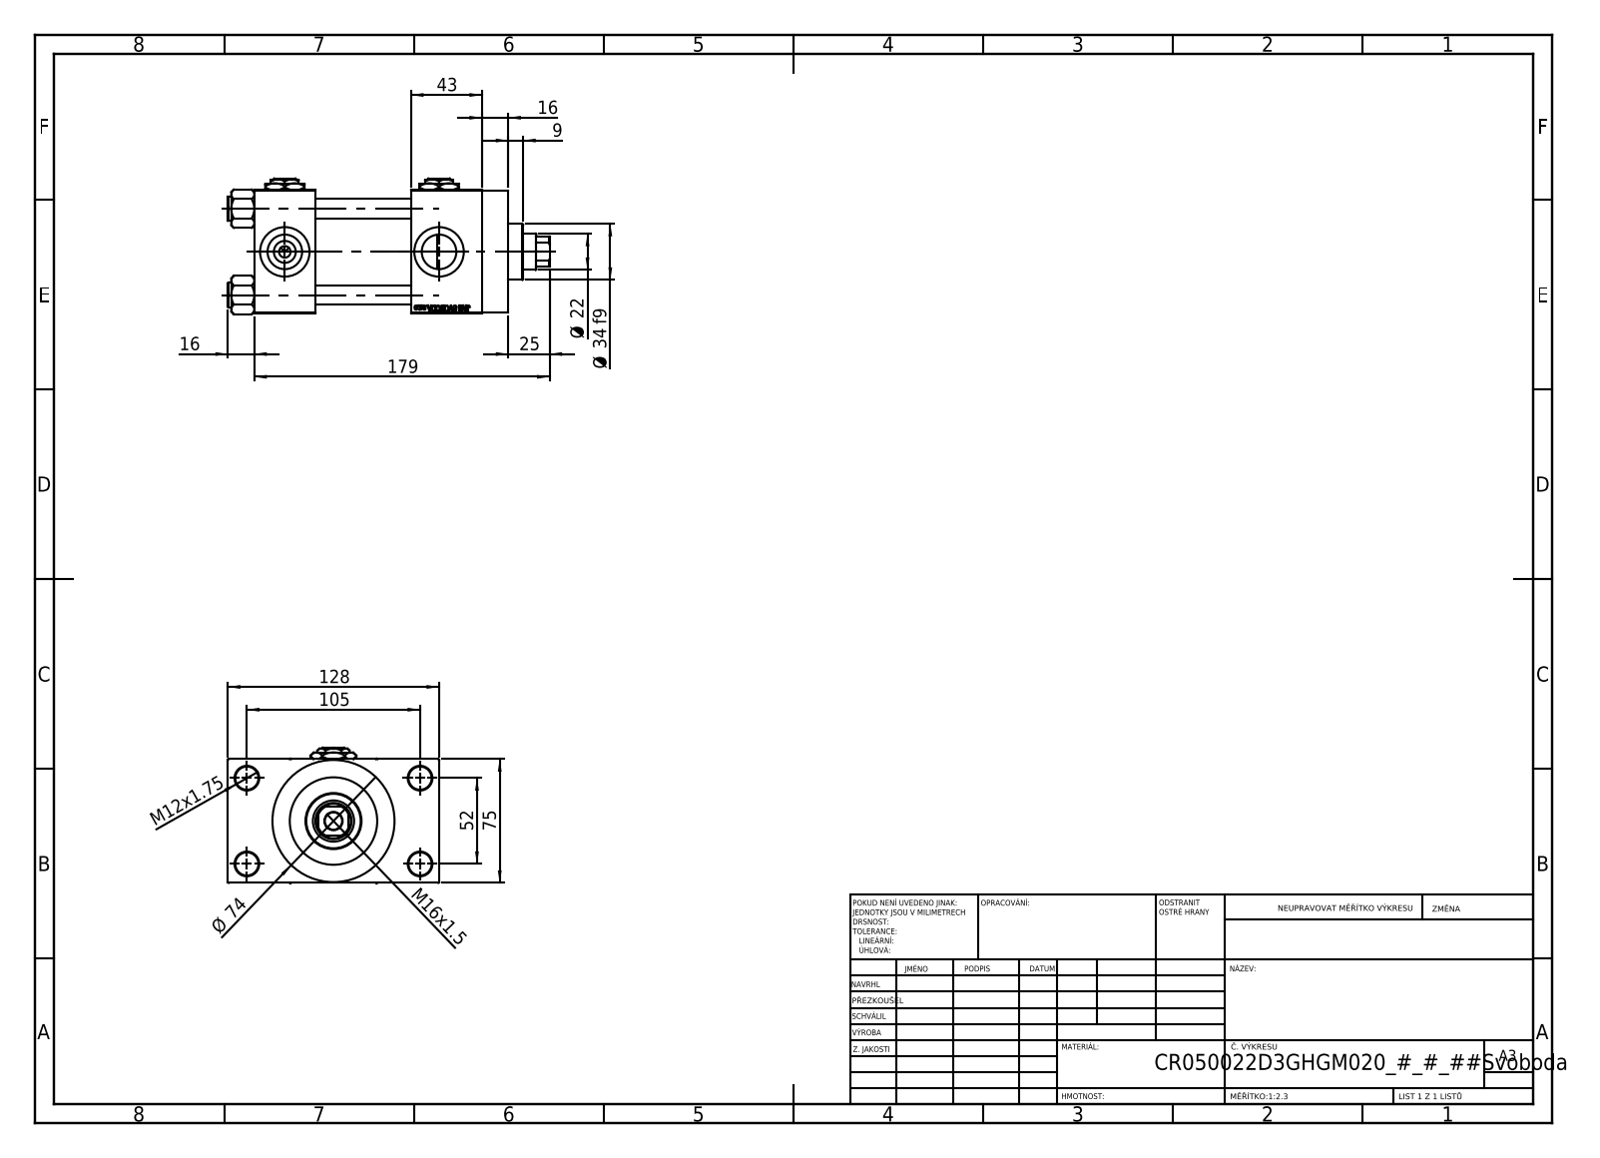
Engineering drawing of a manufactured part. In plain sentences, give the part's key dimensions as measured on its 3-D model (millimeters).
The part is named "Zatka_pro_OIL_PORT; V215_VC_A; V215CR_D_Body; NUT_M5_D (+2 more)". Its 3-D file was written by "SolidWorks 2019 (CONFIG_CONTROL_DESIGN)". It is 13 solids with 1204 faces: 545 planar, 99 cylindrical and 560 other. Overall it measures 195 by 128 by 82.27 millimeters. Its volume is 793 132 cubic millimeters and its surface area 170 921 square millimeters. Round holes: 4 of diameter 12, 4 of diameter 14, 4 of diameter 20.96, 4 of diameter 30, 3 of diameter 7, 1 of diameter 10.5, 1 of diameter 22, 1 of diameter 25, 1 of diameter 41, 1 of diameter 50, 1 of diameter 53. Round bosses or shafts: 4 of diameter 15, 1 of diameter 74, 1 of diameter 56, 1 of diameter 34. Partial cylindrical surfaces (rounded edges, fillets, slot ends): 1 of radius 10.5. The main face-to-face distances are 75, 58, 37, 95, 26.5, 138, 101, 43, 101.5, 16. The hole center spacings are 26.35, 36.98, 52.3, 58.43, 58.59, 78.65, 94.37, 52.
